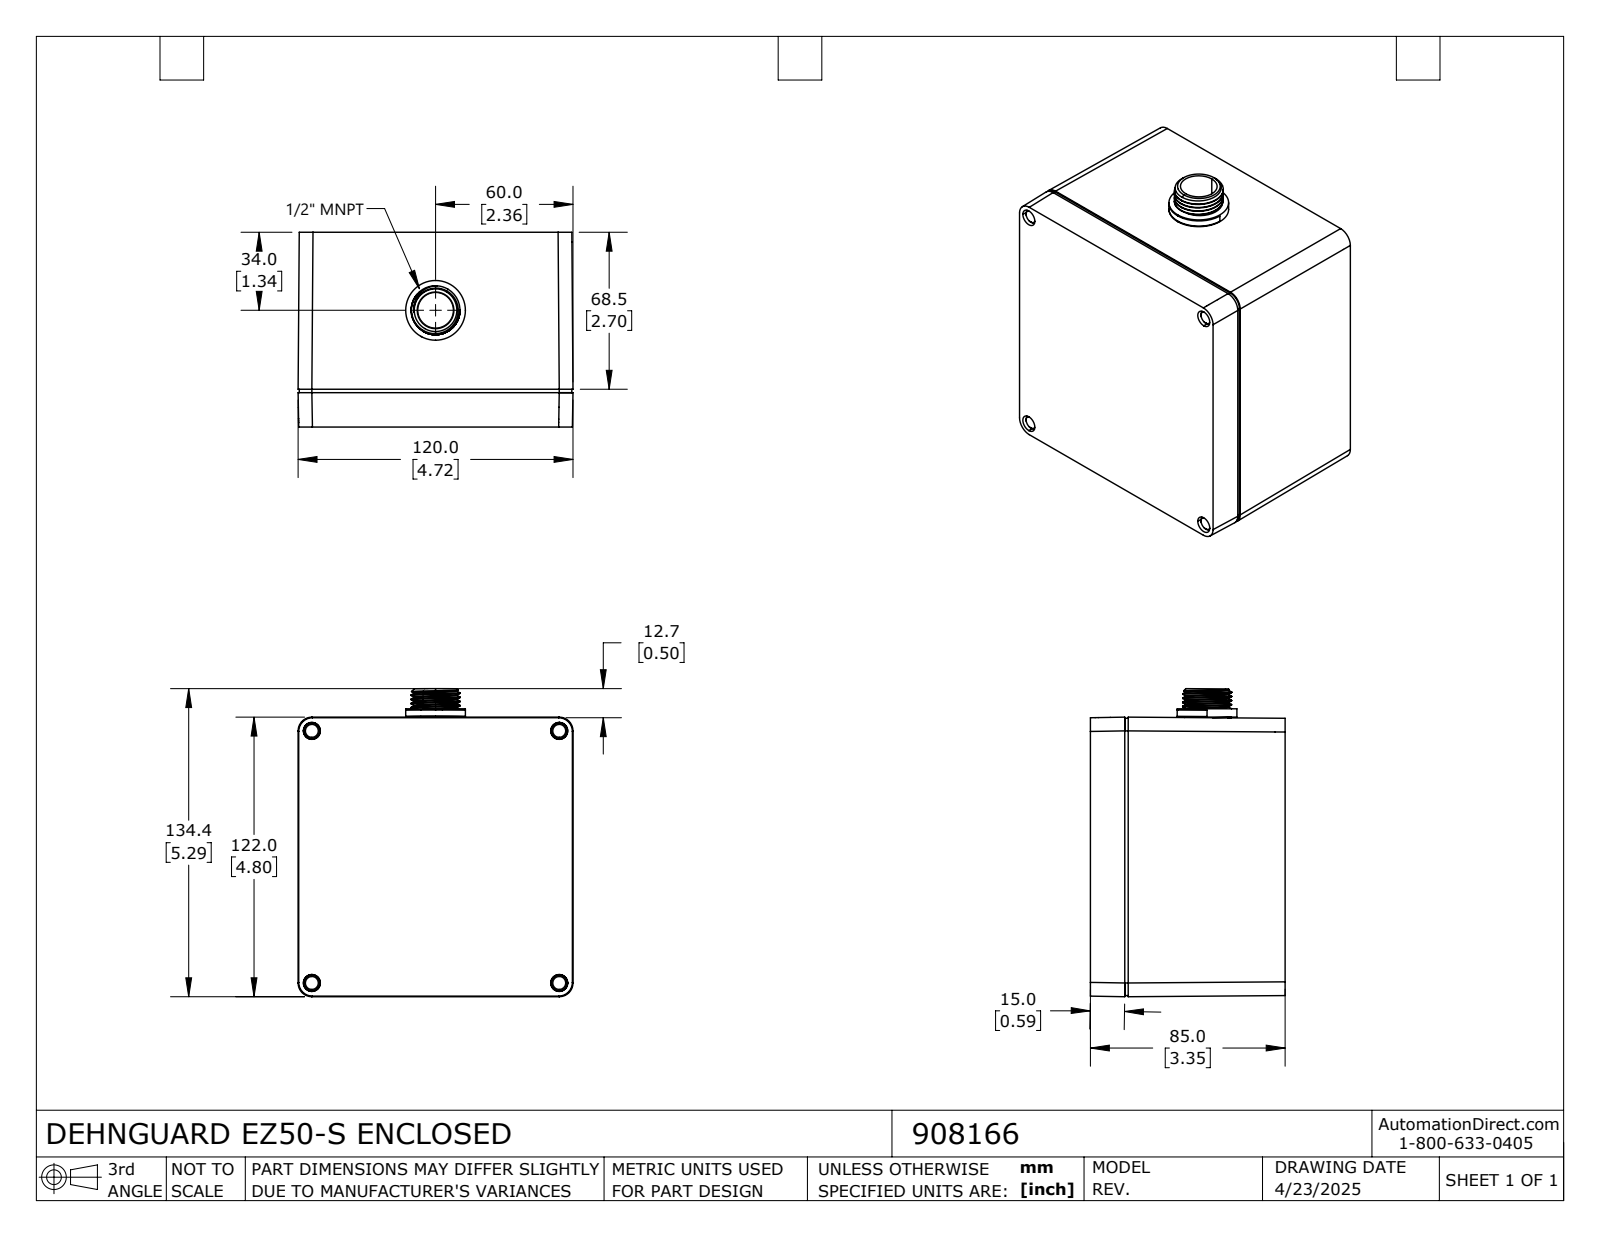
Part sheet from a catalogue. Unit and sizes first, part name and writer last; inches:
Units: inches
Overall size (bounding box): 5.293 × 4.724 × 3.346
Round holes (diameter × count): ⌀0.165 ×4, ⌀0.315 ×4
Round bosses / shafts (diameter × count): ⌀0.276 ×6, ⌀0.113 ×4, ⌀1.166 ×1, ⌀1.125 ×1, ⌀1.026 ×1, ⌀0.84 ×1
Partial cylindrical surfaces — rounded edges, fillets, slot ends (radius × count): R0.004 ×12, R0.047 ×12, R0.236 ×8, R0.217 ×4, R0.02 ×3, R0.008 ×2, R0.016 ×2, R0.03 ×2
Main face-to-face distances: 0.118, 0.157, 3.346, 3.189, 3.228, 3.071, 0.12, 0.039, 0.37, 0.119
Hole centre spacings: 3.543, 4.331, 5.596
Volume: 32.85 in³ · Surface area: 295.3 in²
Bodies: 2 solids, 836 faces (588 planar, 173 cylindrical, 75 other)
Part name (STEP PRODUCT): 908166
STEP written by: SolidWorks 2024 (AUTOMOTIVE_DESIGN)
